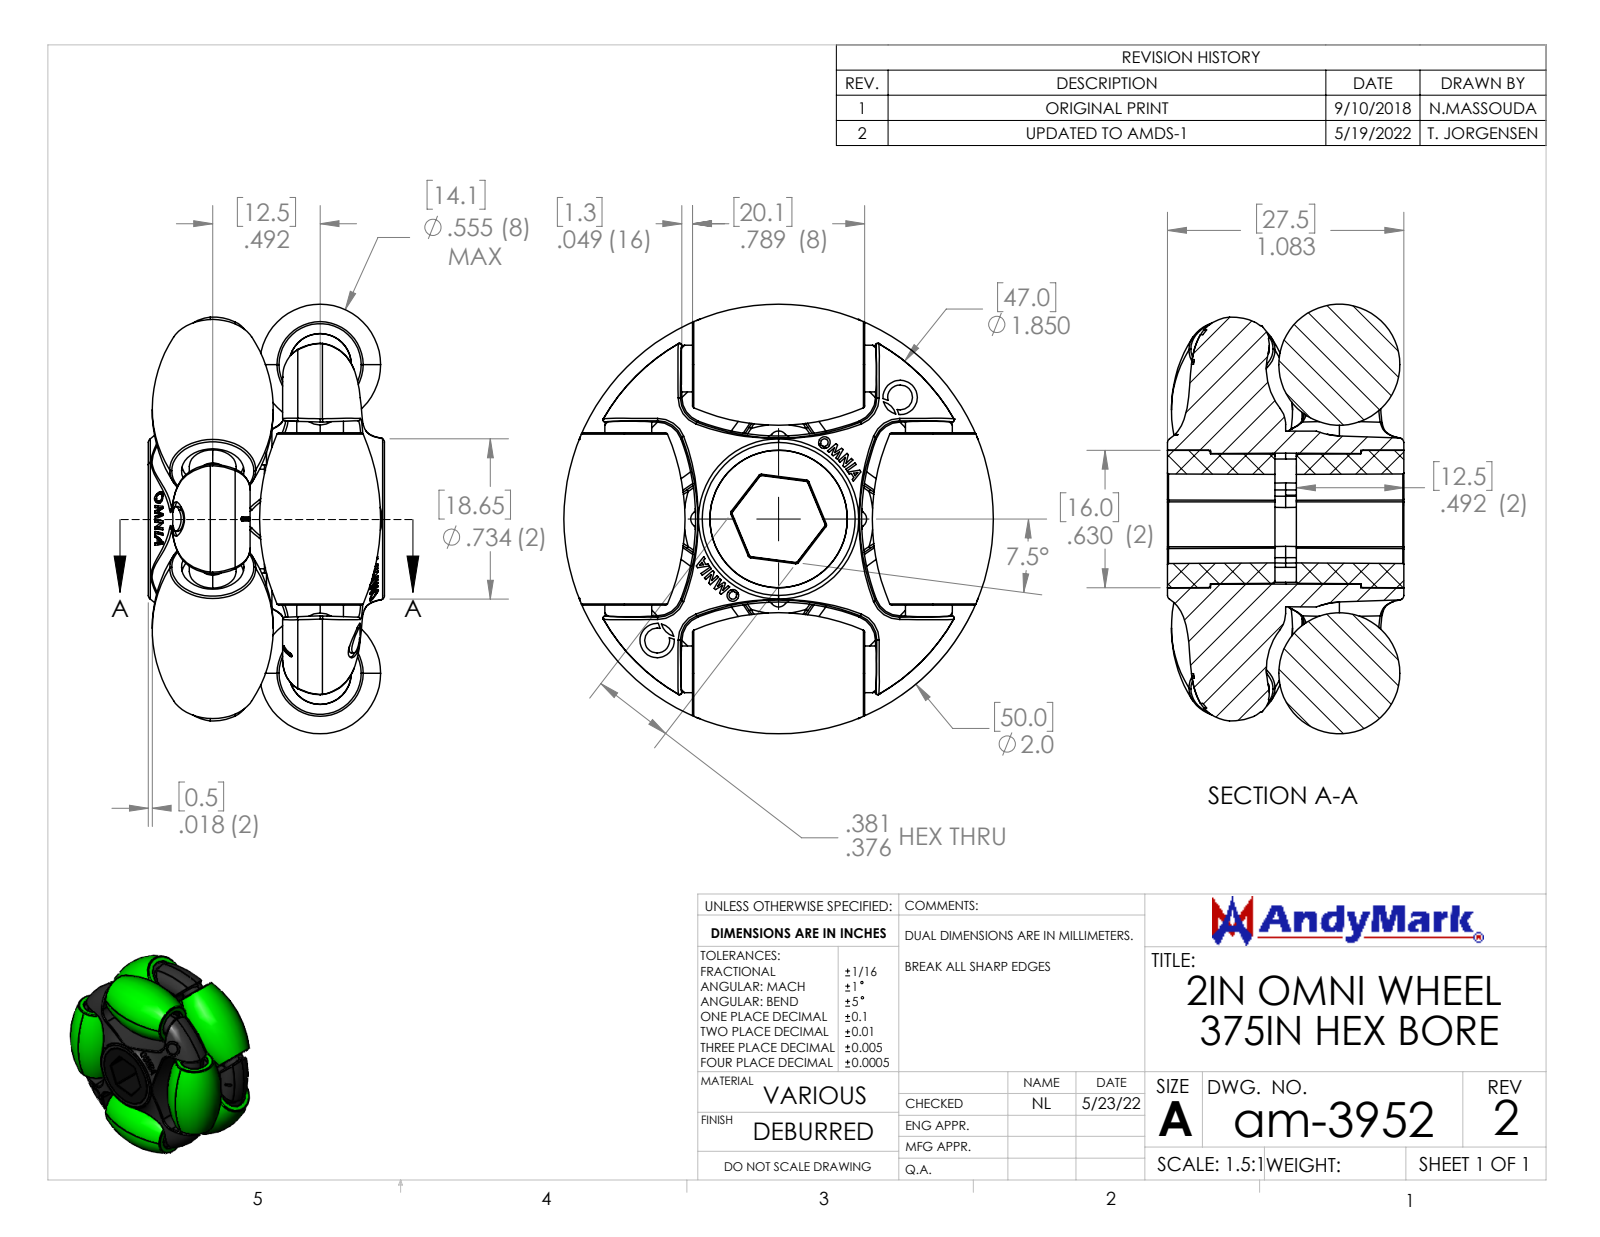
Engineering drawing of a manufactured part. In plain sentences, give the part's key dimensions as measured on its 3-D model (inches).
The part is named "am-3905 14mm Hex to 375in Hex; 2in Omni 14mm Hex; am-3952 2in Omni Wheel 375in Hex Bore". Its 3-D file was written by "SolidWorks 2021 (CONFIG_CONTROL_DESIGN)". It is 3 solids with 1113 faces: 312 planar, 137 cylindrical and 664 other. Overall it measures 1.968 by 1.968 by 1.083 inches. Its volume is 1.972 cubic inches and its surface area 26.83 square inches. Round holes: 4 of diameter 0.157, 1 of diameter 0.63. Round bosses or shafts: 6 of diameter 0.214, 4 of diameter 0.114, 2 of diameter 0.215. Partial cylindrical surfaces (rounded edges, fillets, slot ends): 12 of radius 0.004, 12 of radius 0.01, 8 of radius 0.008, 4 of radius 0.027, 4 of radius 0.033, 4 of radius 0.079, 4 of radius 0.092, 1 of radius 0.291. The main face-to-face distances are 0.461, 0.086, 0.55, 0.09, 0.464, 0.547, 0.743, 0.046, 0.086, 0.374. The hole center spacings are 0.787, 1.575, 0.603, 0.603, 1.455, 1.455.
